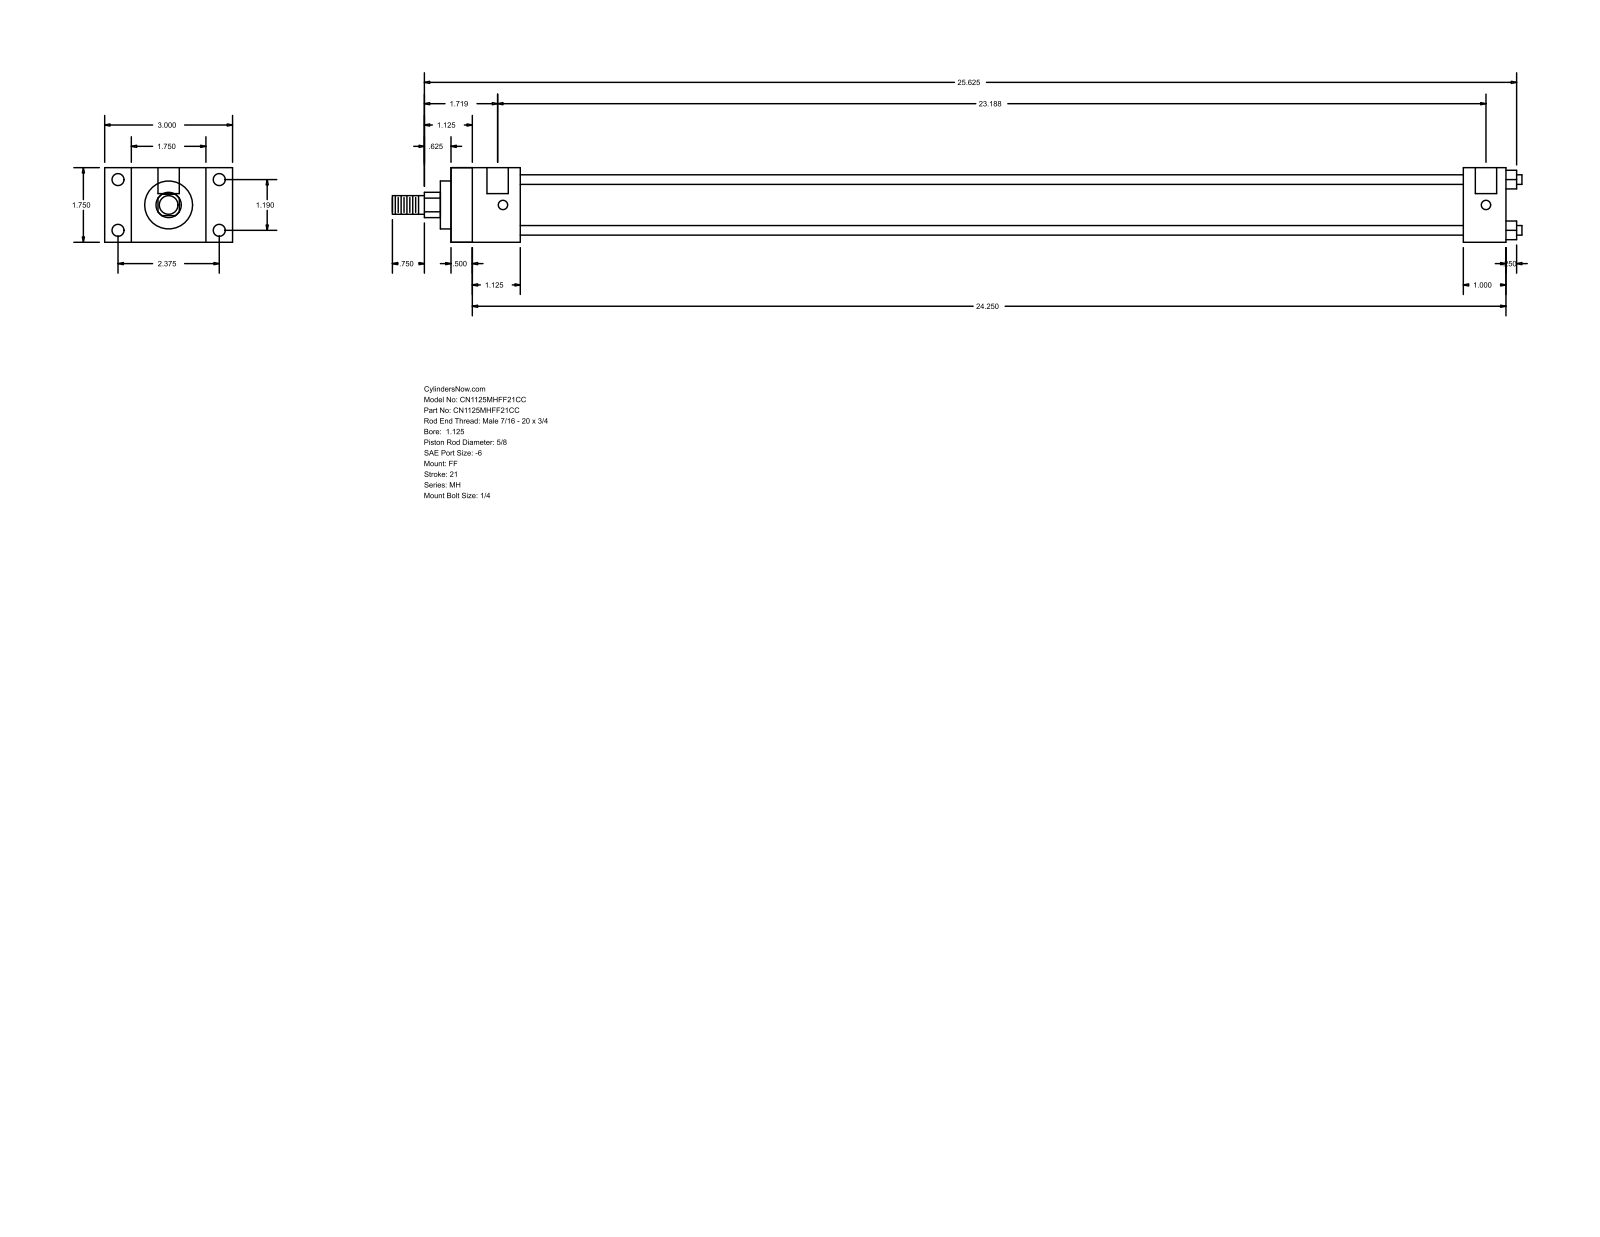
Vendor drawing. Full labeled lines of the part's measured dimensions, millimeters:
Part name (STEP PRODUCT): MH_FF__0112_0.625
STEP written by: GSSL Pune (CONFIG_CONTROL_DESIGN)
Units: millimetres
Bodies: 0 solids, 92 faces (64 planar, 28 cylindrical, 0 other)
Overall size (bounding box): 673.1 × 76.2 × 44.45
Round holes (diameter × count): ⌀5.56 ×4, ⌀7.14 ×4, ⌀12.7 ×2
Round bosses / shafts (diameter × count): ⌀5.71 ×4, ⌀34.92 ×1, ⌀28.57 ×1, ⌀15.88 ×1, ⌀11.11 ×1
Partial cylindrical surfaces — rounded edges, fillets, slot ends (radius × count): R7.54 ×1
Main face-to-face distances: 44.46, 628.64, 12.69, 615.95, 15.87, 28.58, 60.33, 25.4, 41.27, 603.24
Hole centre spacings: 30.22, 60.32, 67.47, 585.79, 3.17, 588.96
